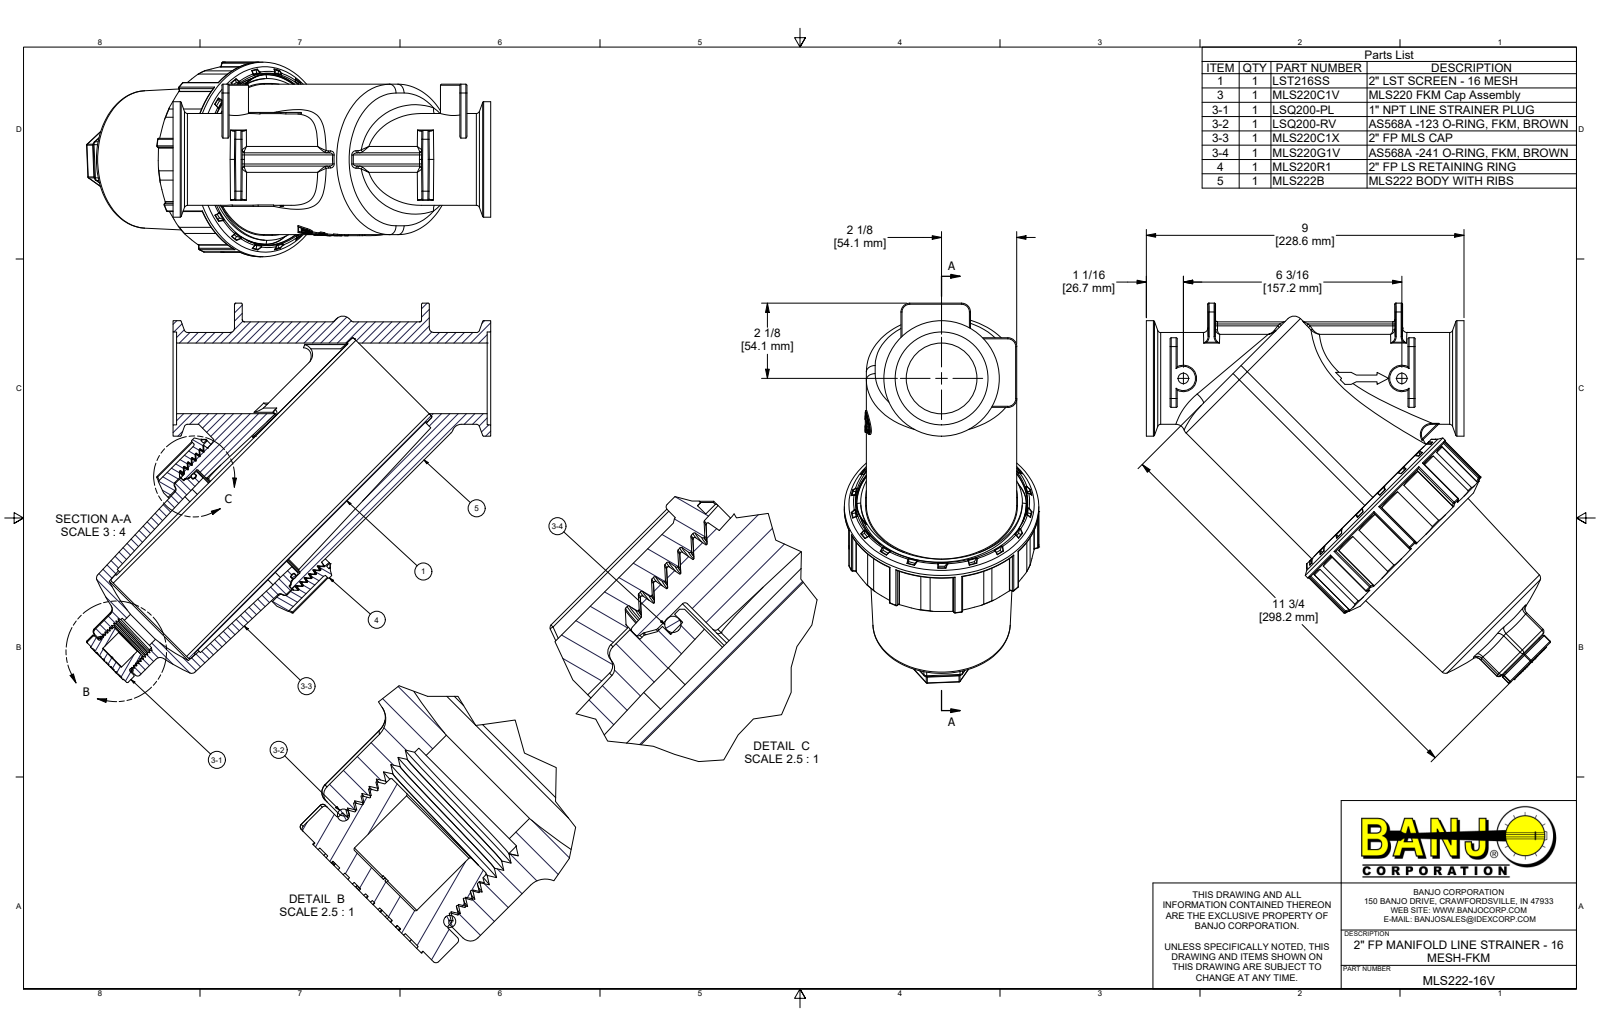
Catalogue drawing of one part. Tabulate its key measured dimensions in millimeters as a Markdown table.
| quantity | value |
| --- | --- |
| part name | MLS222-16V; MLS222B; MLS220C1V; MLS220C1X (+7 more) |
| STEP written by | Autodesk Inventor 2019 (AUTOMOTIVE_DESIGN) |
| units | millimeters |
| bodies | 9 solids, 2342 faces (1017 planar, 364 cylindrical, 961 other) |
| overall size | 290.9 × 273.3 × 140 |
| volume | 1 481 000 mm³ |
| surface area | 477 200 mm² |
| round holes (diameter × count) | 7.5 × 2, 11.5 × 1, 16.3 × 1, 19.1 × 1, 25.4 × 1, 29.9 × 1, 50.8 × 1, 66.8 × 1, 74.6 × 1, 89.7 × 1, 104.9 × 1, 106 × 1 |
| round bosses / shafts (diameter × count) | 81 × 2, 140 × 1, 133.4 × 1, 113 × 1, 107.1 × 1, 104.1 × 1, 99.2 × 1, 83.1 × 1 |
| partial cylindrical surfaces (radius × count) | 0.8 × 80, 0.3 × 36, 1.5 × 12, 2.3 × 12, 6.4 × 8, 3.2 × 6, 0.8 × 4, 0.5 × 2 |
| main face-to-face distances | 2.5, 226.1, 7.6, 228.6, 147.5, 155.2, 134.6, 5.1, 171.2, 27.8 |
| hole center spacings | 64.1, 106.5, 157.2 |
